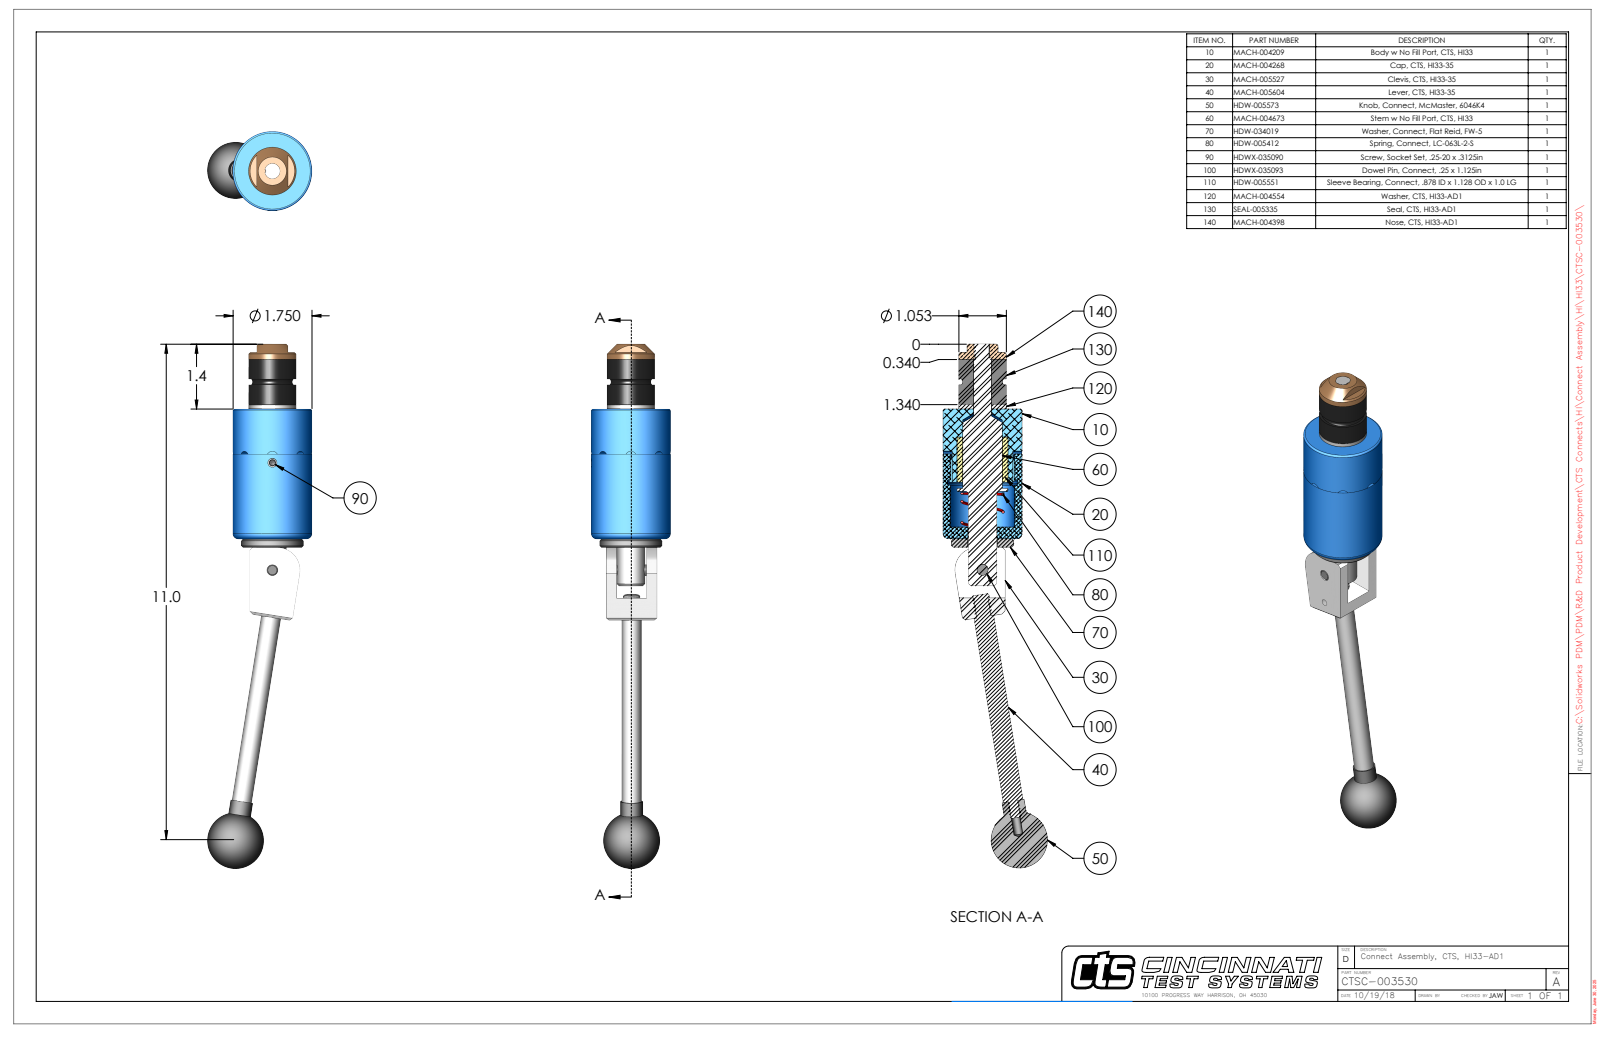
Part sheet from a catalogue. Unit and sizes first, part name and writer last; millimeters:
Units: millimetres
Overall size (bounding box): 295 × 58.7 × 44.5
Round holes (diameter × count): ⌀5.1 ×2, ⌀8 ×2, ⌀3.8 ×1, ⌀6.3 ×1, ⌀6.4 ×1, ⌀9.9 ×1, ⌀10.1 ×1, ⌀10.2 ×1, ⌀16.1 ×1, ⌀16.7 ×1, ⌀36 ×1
Round bosses / shafts (diameter × count): ⌀9.5 ×2, ⌀7.9 ×2, ⌀6.4 ×2, ⌀44.5 ×1, ⌀35.1 ×1, ⌀26.7 ×1, ⌀15.9 ×1, ⌀12.7 ×1
Partial cylindrical surfaces — rounded edges, fillets, slot ends (radius × count): R3.2 ×4, R0.7 ×2, R12.7 ×1, R17.7 ×1, R21 ×1
Main face-to-face distances: 73.1, 27.9, 25.4, 101, 2.5, 75.6, 28.4, 105.8, 80.4, 77.9
Hole centre spacings: 18.8, 60.4, 79.1
Volume: 184 800 mm³ · Surface area: 41 250 mm²
Bodies: 9 solids, 233 faces (78 planar, 96 cylindrical, 59 other)
Part name (STEP PRODUCT): CTSC-003530
STEP written by: SolidWorks 2023 (AUTOMOTIVE_DESIGN)
